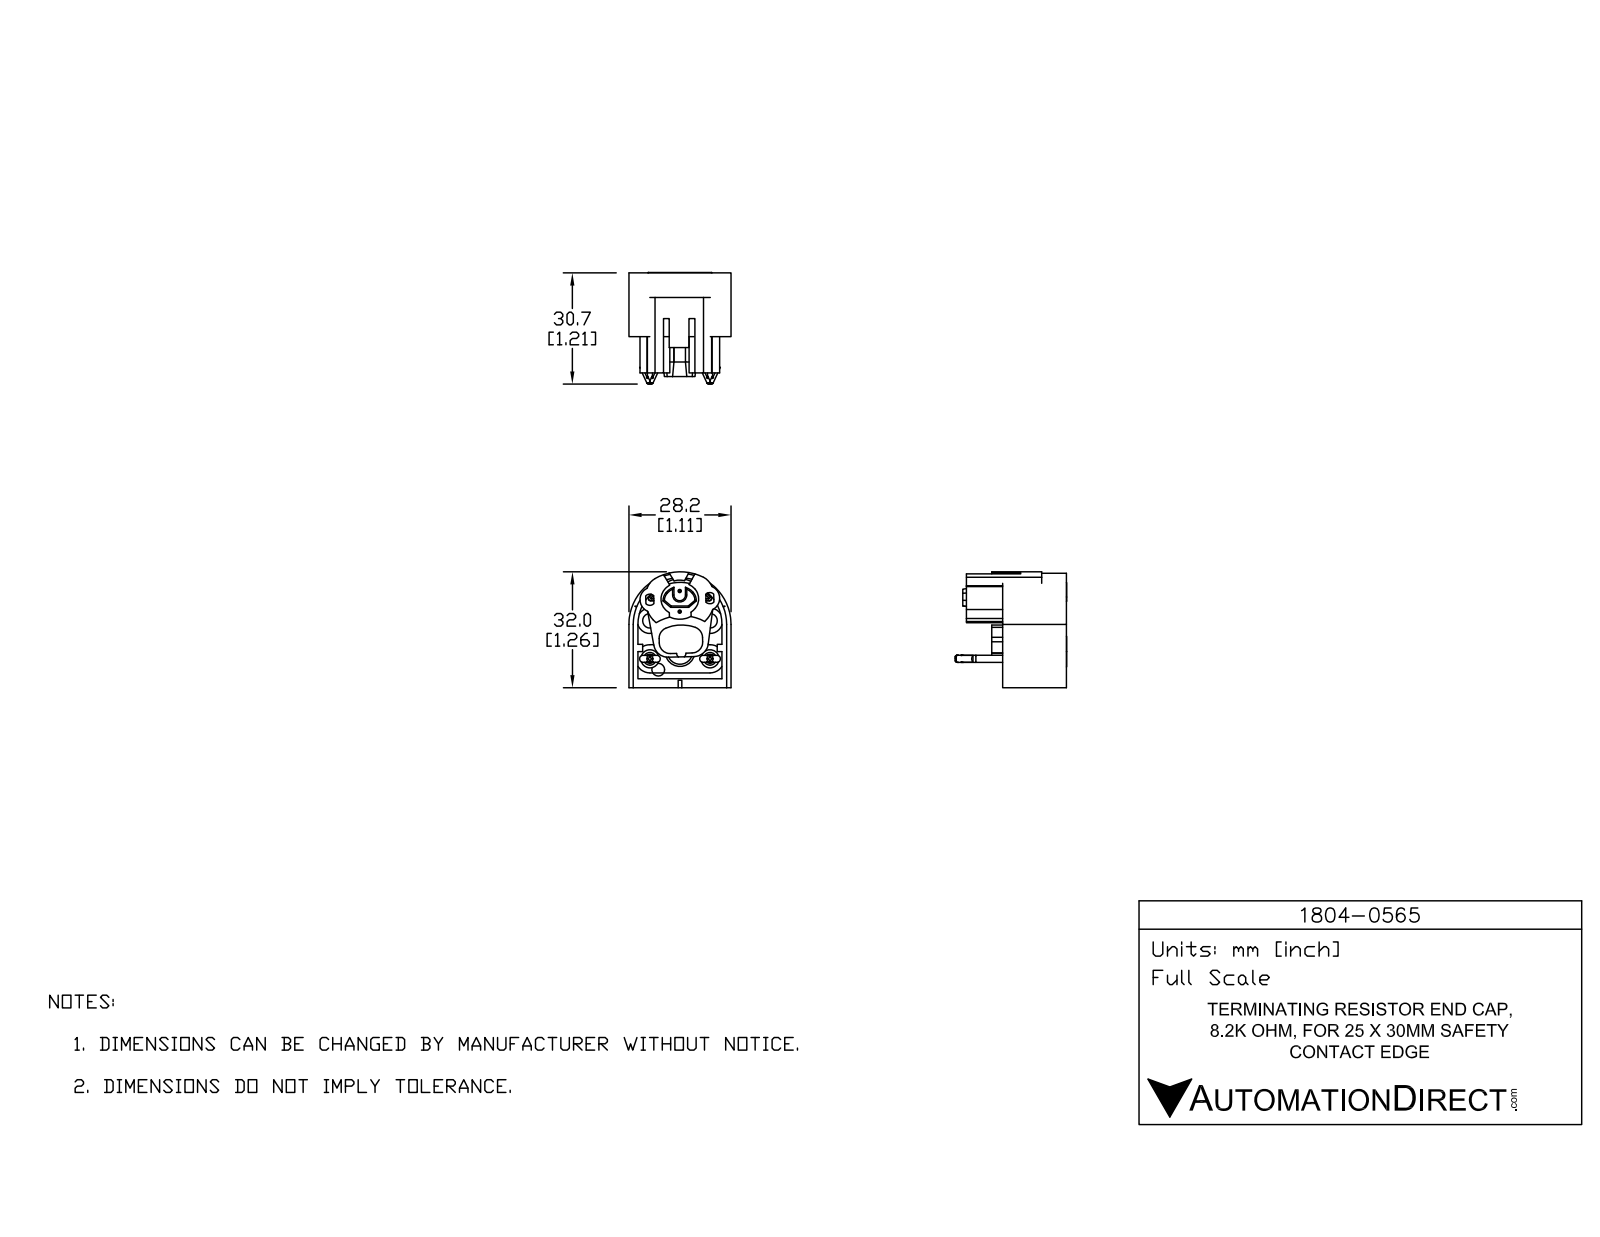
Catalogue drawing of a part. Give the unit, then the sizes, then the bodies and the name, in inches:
Units: inches
Overall size (bounding box): 1.244 × 1.213 × 1.11
Round holes (diameter × count): ⌀0.02 ×4, ⌀0.138 ×3, ⌀0.028 ×2, ⌀0.035 ×2, ⌀0.122 ×2, ⌀0.157 ×2, ⌀0.217 ×2
Round bosses / shafts (diameter × count): ⌀0.197 ×2, ⌀0.138 ×2, ⌀0.098 ×2, ⌀0.079 ×2, ⌀0.059 ×2, ⌀0.024 ×2
Partial cylindrical surfaces — rounded edges, fillets, slot ends (radius × count): R0.039 ×8, R0.118 ×6, R0.138 ×6, R0.157 ×4, R0.197 ×4, R0.154 ×2, R0.161 ×2, R0.201 ×2
Main face-to-face distances: 0.071, 0.098, 0.039, 0.031, 0.425, 1.11, 0.228, 0.051, 0.457, 0.197
Hole centre spacings: 0.654, 0.055, 0.348, 0.224, 0.341, 0.343, 0.343, 0.344
Volume: 0.591 in³ · Surface area: 16.28 in²
Bodies: 6 solids, 369 faces (158 planar, 155 cylindrical, 56 other)
Part name (STEP PRODUCT): END CAP - SENTIR EDGE 25.30 KS4 - SINGLE CLIP; 1804-0380-Klemmstück; 1804-0565; 1804-0440-Rasttraverse (+1 more)
STEP written by: SolidWorks 2017 (AUTOMOTIVE_DESIGN)
